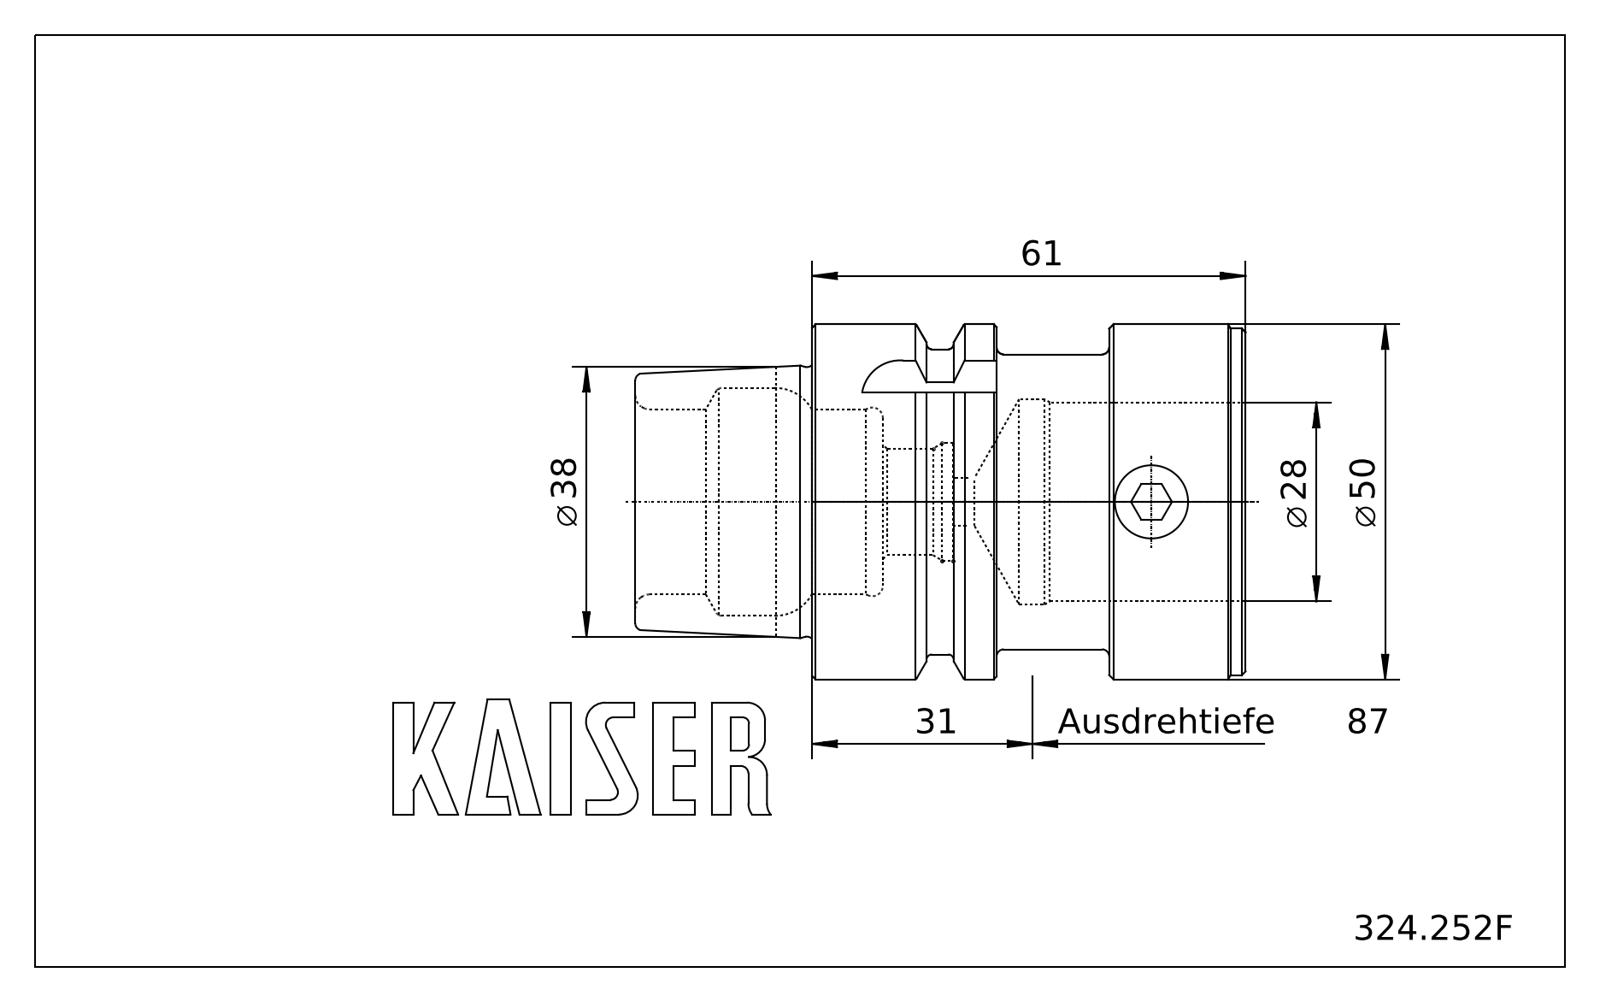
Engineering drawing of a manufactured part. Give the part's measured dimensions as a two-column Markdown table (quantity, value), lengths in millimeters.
| quantity | value |
| --- | --- |
| part name | 324.252F Kaiser HSK-A50xCK5x87\|690.435 Kaiser ETL M10 X 14 CK5;Schnitt-Linear austragen2; 324.252F Kaiser HSK-A50xCK5x87\|324.252F Kaiser HSK-A50xCK5x87;Verrundung1 |
| STEP written by | ACIS (automotive_design) |
| units | millimeters |
| bodies | 2 solids, 285 faces (85 planar, 62 cylindrical, 138 other) |
| overall size | 85.9 × 50 × 50 |
| volume | 84 676 mm³ |
| surface area | 24 858 mm² |
| round holes (diameter × count) | 6 × 1, 6.8 × 1, 9.04 × 1, 10.06 × 1, 10.3 × 1, 10.55 × 1, 15 × 1, 16.5 × 1, 26.04 × 1, 28 × 1, 28.5 × 1, 32.08 × 1 |
| round bosses / shafts (diameter × count) | 50 × 1, 49.95 × 1, 48.8 × 1, 42.95 × 1, 41.5 × 1, 10 × 1 |
| partial cylindrical surfaces (radius × count) | 1.4 × 6, 6 × 5, 2.38 × 4, 4.5 × 2 |
| main face-to-face distances | 61, 19, 42, 35.05, 16.05, 25.95, 51.05, 32.05, 16, 9.95 |
| hole center spacings | 40.95 |
